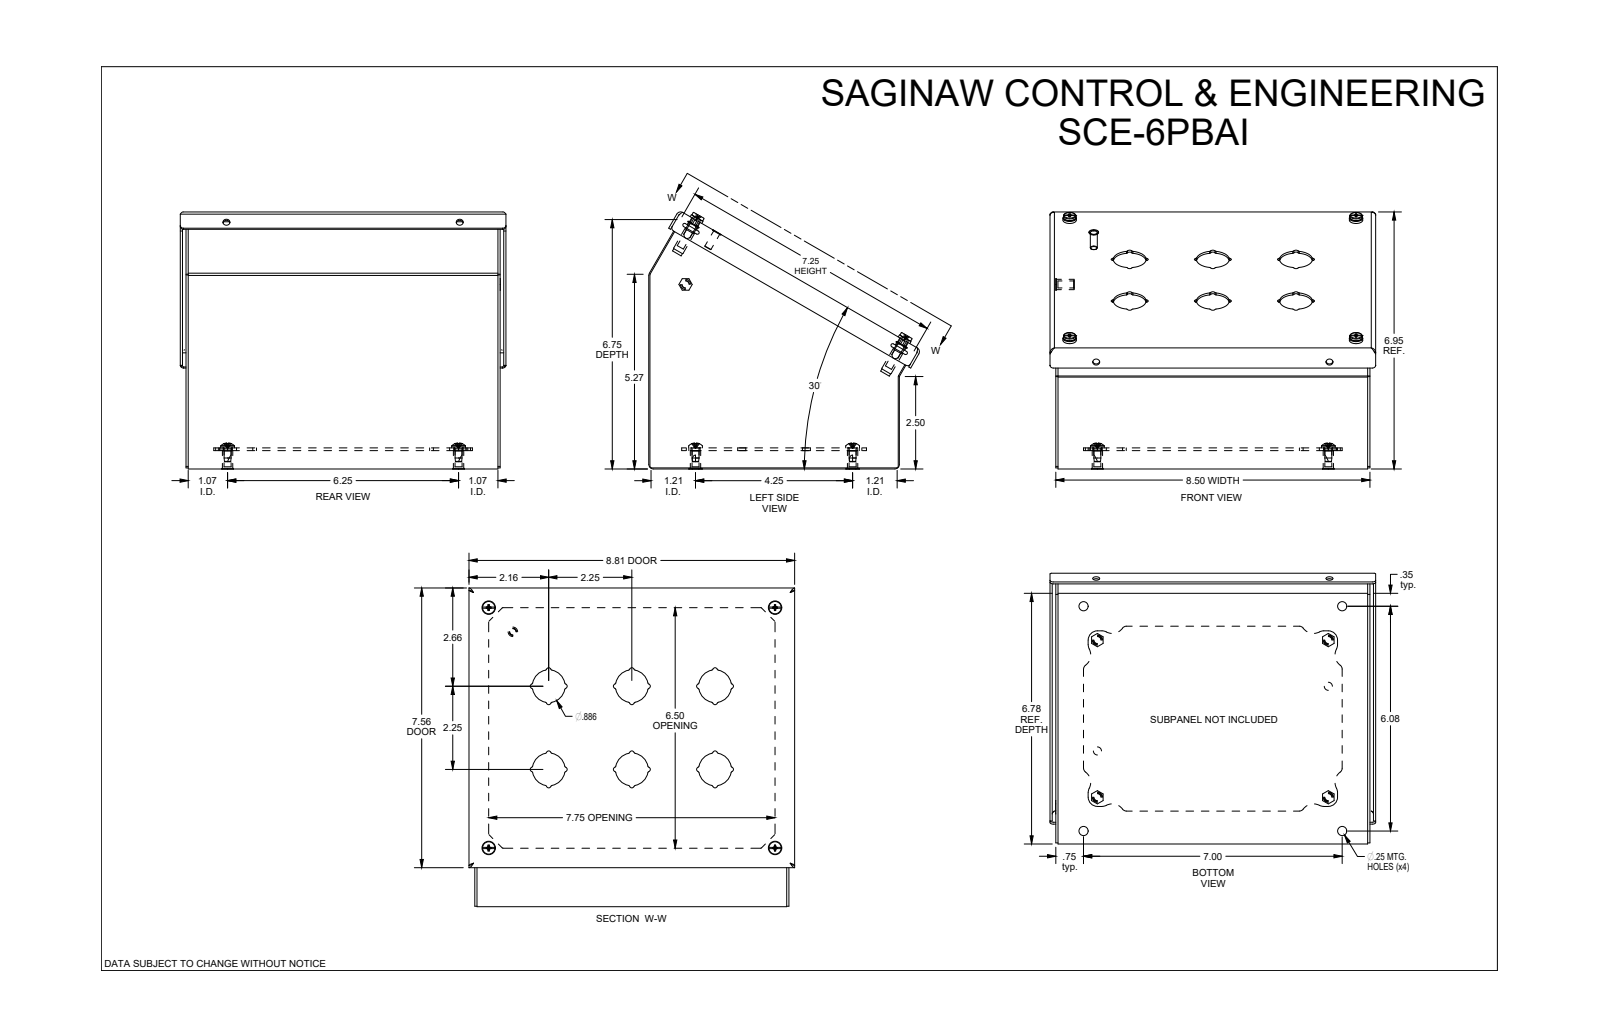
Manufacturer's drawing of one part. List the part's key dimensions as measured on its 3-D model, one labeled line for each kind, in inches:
Part name (STEP PRODUCT): SCE-6PBAI
STEP written by: SolidWorks 2021 (AUTOMOTIVE_DESIGN)
Units: inches
Bodies: 7 solids, 607 faces (208 planar, 335 cylindrical, 64 other)
Overall size (bounding box): 8.813 × 7.345 × 6.978
Volume: 21.42 in³ · Surface area: 702.8 in²
Round holes (diameter × count): ⌀0.25 ×12, ⌀0.19 ×9, ⌀0.22 ×4, ⌀0.266 ×4, ⌀0.218 ×2
Round bosses / shafts (diameter × count): ⌀0.28 ×5, ⌀0.362 ×4, ⌀0.34 ×4, ⌀0.292 ×4, ⌀0.27 ×4, ⌀0.26 ×4, ⌀0.256 ×1, ⌀0.188 ×1
Partial cylindrical surfaces — rounded edges, fillets, slot ends (radius × count): R0.04 ×48, R0.062 ×24, R0.125 ×12, R0.25 ×12, R0.01 ×8, R0.03 ×8, R0.06 ×8, R0.115 ×8
Main face-to-face distances: 0.06, 8.44, 6.72, 8.5, 8.38, 0.436, 0.496, 0.571, 0.511, 0.075
Hole centre spacings: 6.5, 7.75, 0.989, 5.178, 6.688, 8.401, 6.505, 7.75
